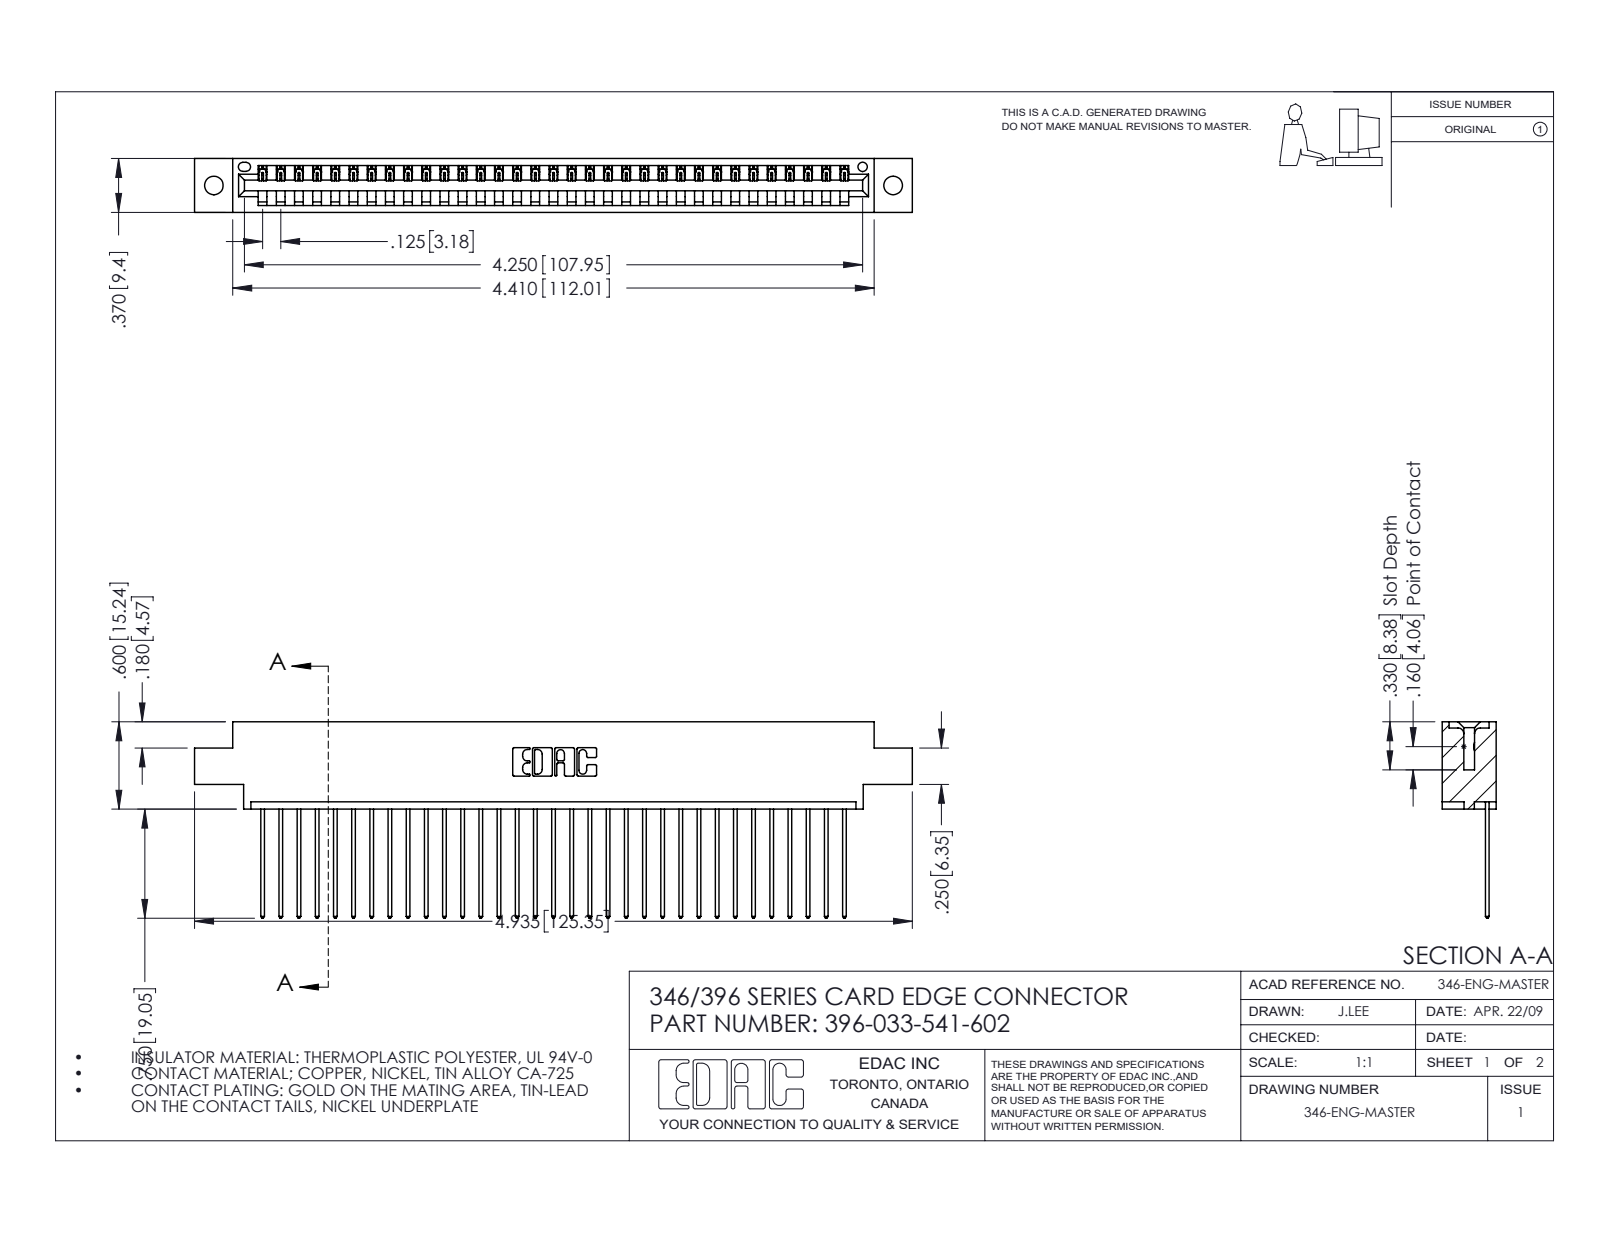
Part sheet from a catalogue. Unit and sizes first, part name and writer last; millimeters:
Units: millimetres
Overall size (bounding box): 125.3 × 34.3 × 9.4
Round holes (diameter × count): ⌀3.3 ×2, ⌀1.6 ×1
Partial cylindrical surfaces — rounded edges, fillets, slot ends (radius × count): R0.2 ×66, R0.3 ×66, R0.3 ×22, R0.2 ×6, R0.8 ×6, R0.7 ×3, R0.8 ×2, R1 ×2
Main face-to-face distances: 1.2, 8.2, 9.4, 6.4, 1.8, 7.6, 0.6, 3.8, 5.6, 2.5
Hole centre spacings: 6.2, 113.3, 118.6
Volume: 11 800 mm³ · Surface area: 15 260 mm²
Bodies: 34 solids, 2040 faces (1400 planar, 640 cylindrical, 0 other)
Part name (STEP PRODUCT): 345-292-001_345-293-141; 346 Part_0.170 Offset - 0.128 Dia; 396-033-541-602
STEP written by: SolidWorks 2016 (CONFIG_CONTROL_DESIGN)
